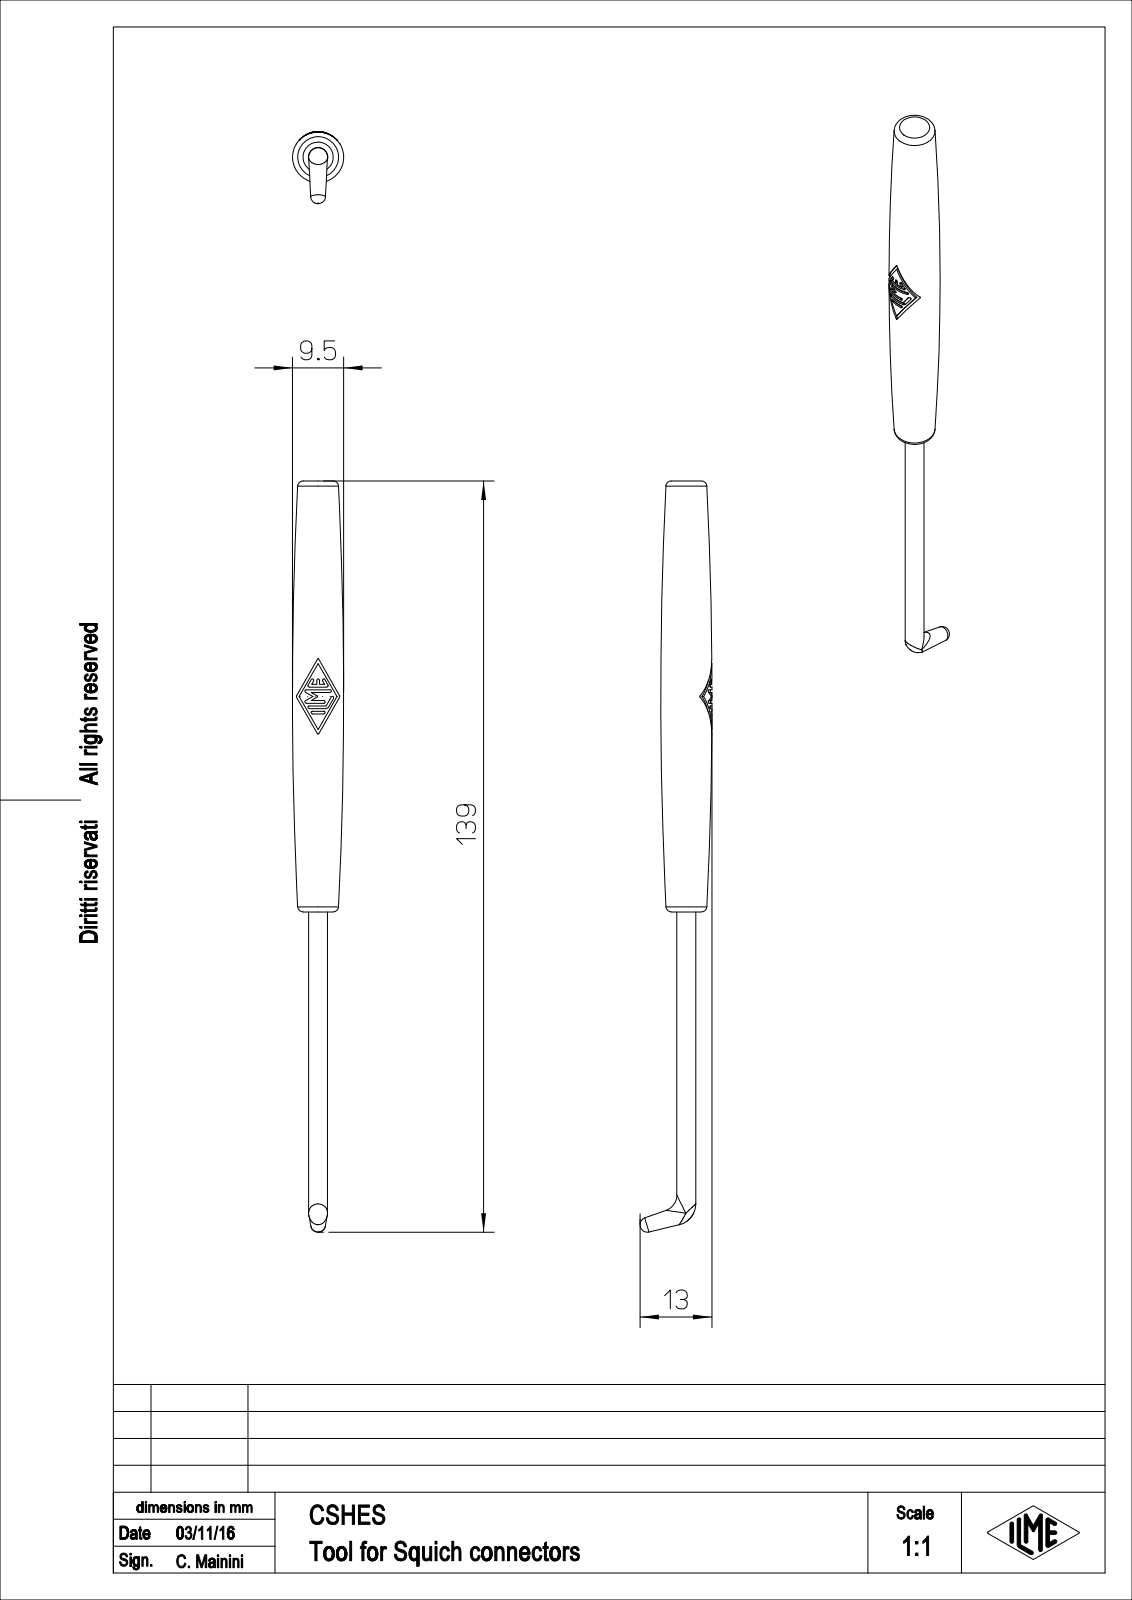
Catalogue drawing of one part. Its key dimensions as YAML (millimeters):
part_name: "CSHES"
step_written_by: "PTC Creo Elements/Direct Modeling 19.0E 27-Jun-2016 (C) Parametric Technology GmbH (AUTOMOTIVE_DESIGN)"
units: millimeters
bodies: {solids: 1, faces: 79, planar: 35, cylindrical: 22, other: 22}
overall_size: [139.43, 13.32, 9.5]
volume: 5493
surface_area: 3993
round_holes:
  - {diameter: 3.6, count: 1}
round_bosses_or_shafts:
  - {diameter: 3.5, count: 1}
partial_cylinders:
  - {radius: 0.25, count: 13}
  - {radius: 0.12, count: 3}
  - {radius: 0.5, count: 1}
face_to_face_distances: [0.5, 80, 6.58, 7.08, 1, 6.08, 3, 2.5, 1.5, 3.5]
